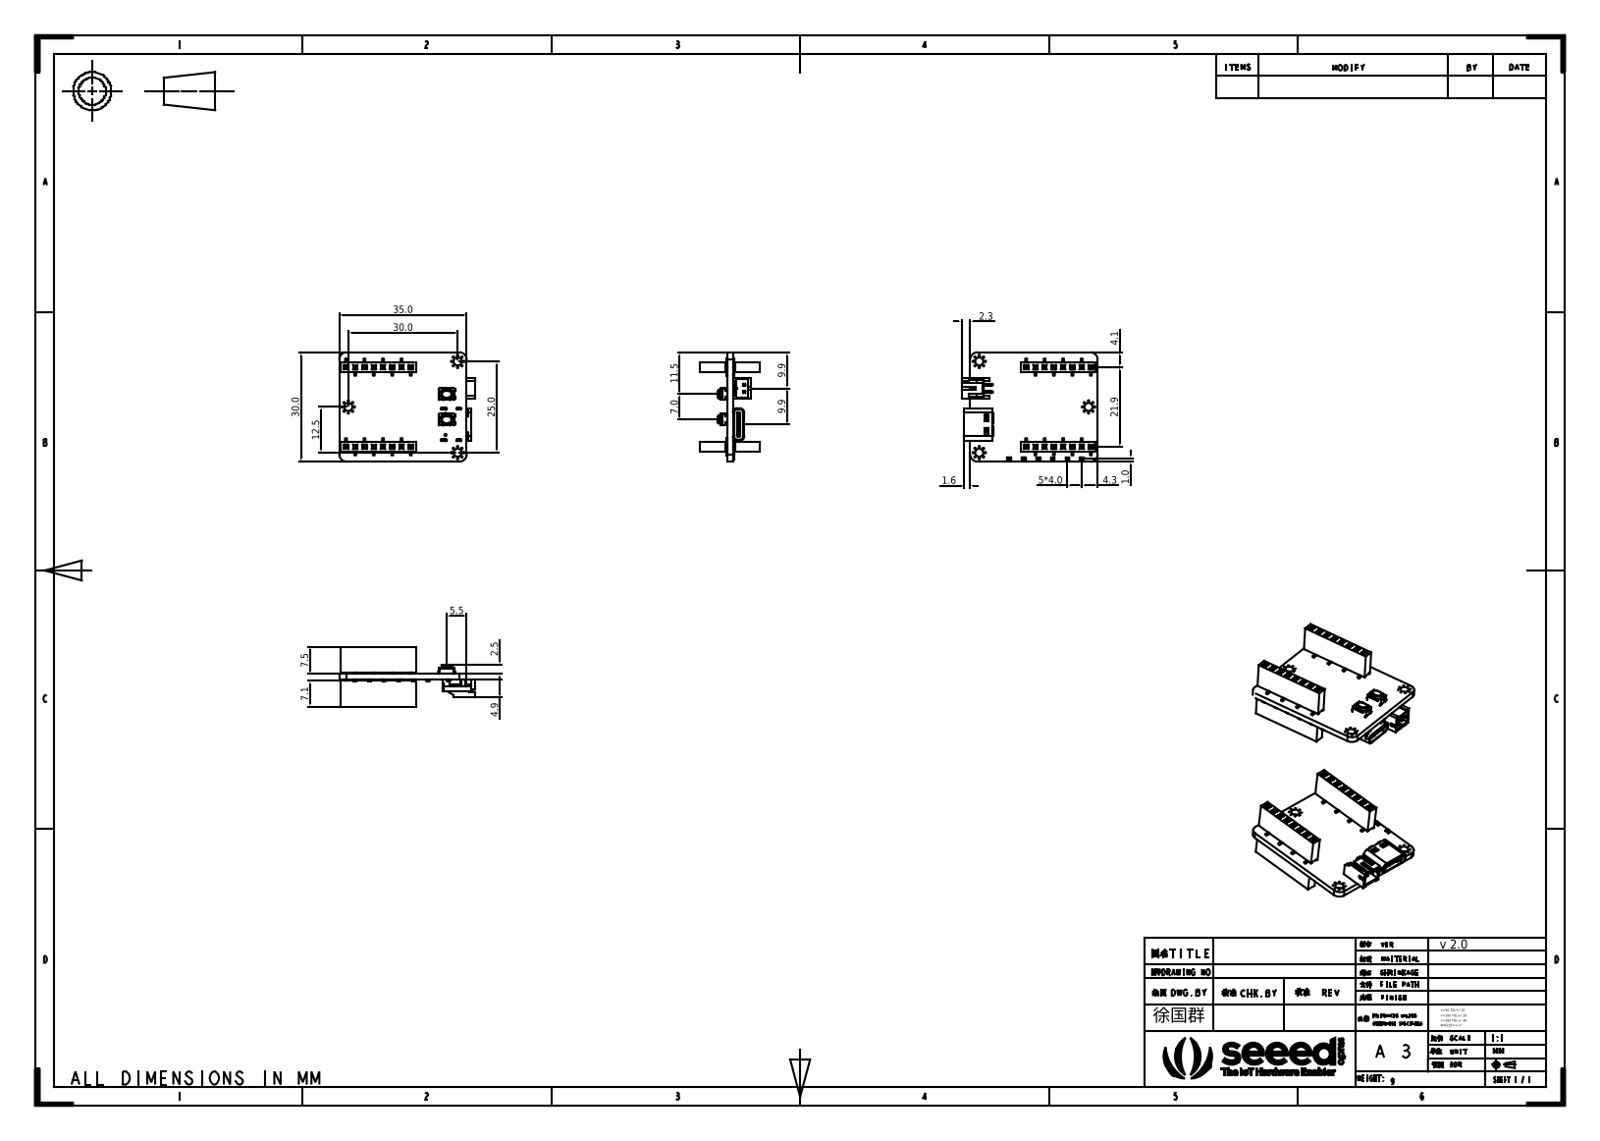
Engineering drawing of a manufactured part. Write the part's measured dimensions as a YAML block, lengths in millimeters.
part_name: "Type C; COMPOUND; COMPOUND183104; 按键1 (+5 more)"
step_written_by: "SIEMENS PLM Software NX 12.0 (AP203_CONFIGURATION_CONTROLLED_3D_DESIGN_OF_MECHANICAL_PARTS_AND_ASSEMBLIES_MIM_LF)"
units: millimeters
bodies: {solids: 37, faces: 2340, planar: 1796, cylindrical: 471, other: 73}
overall_size: [53.73, 50, 17.5]
volume: 14643
surface_area: 20516
round_holes:
  - {diameter: 0.4, count: 26}
  - {diameter: 0.3, count: 12}
  - {diameter: 1.2, count: 6}
  - {diameter: 0.6, count: 4}
  - {diameter: 2.2, count: 3}
  - {diameter: 4.2, count: 1}
  - {diameter: 6.7, count: 1}
round_bosses_or_shafts:
  - {diameter: 7.2, count: 1}
  - {diameter: 6.3, count: 1}
  - {diameter: 6, count: 1}
  - {diameter: 5.2, count: 1}
  - {diameter: 2.8, count: 1}
  - {diameter: 0.84, count: 1}
partial_cylinders:
  - {radius: 0.5, count: 34}
  - {radius: 0.51, count: 32}
  - {radius: 0.2, count: 16}
  - {radius: 0.3, count: 16}
  - {radius: 1, count: 12}
  - {radius: 0.1, count: 9}
  - {radius: 1.1, count: 8}
  - {radius: 1.2, count: 8}
face_to_face_distances: [1.8, 2, 17.5, 15.5, 15.7, 13.7, 9.6, 8, 7.7, 33.2]
hole_center_spacings: [1.26, 1.65, 3.05, 2.33, 2.34, 32.52, 25.04, 32.5]
